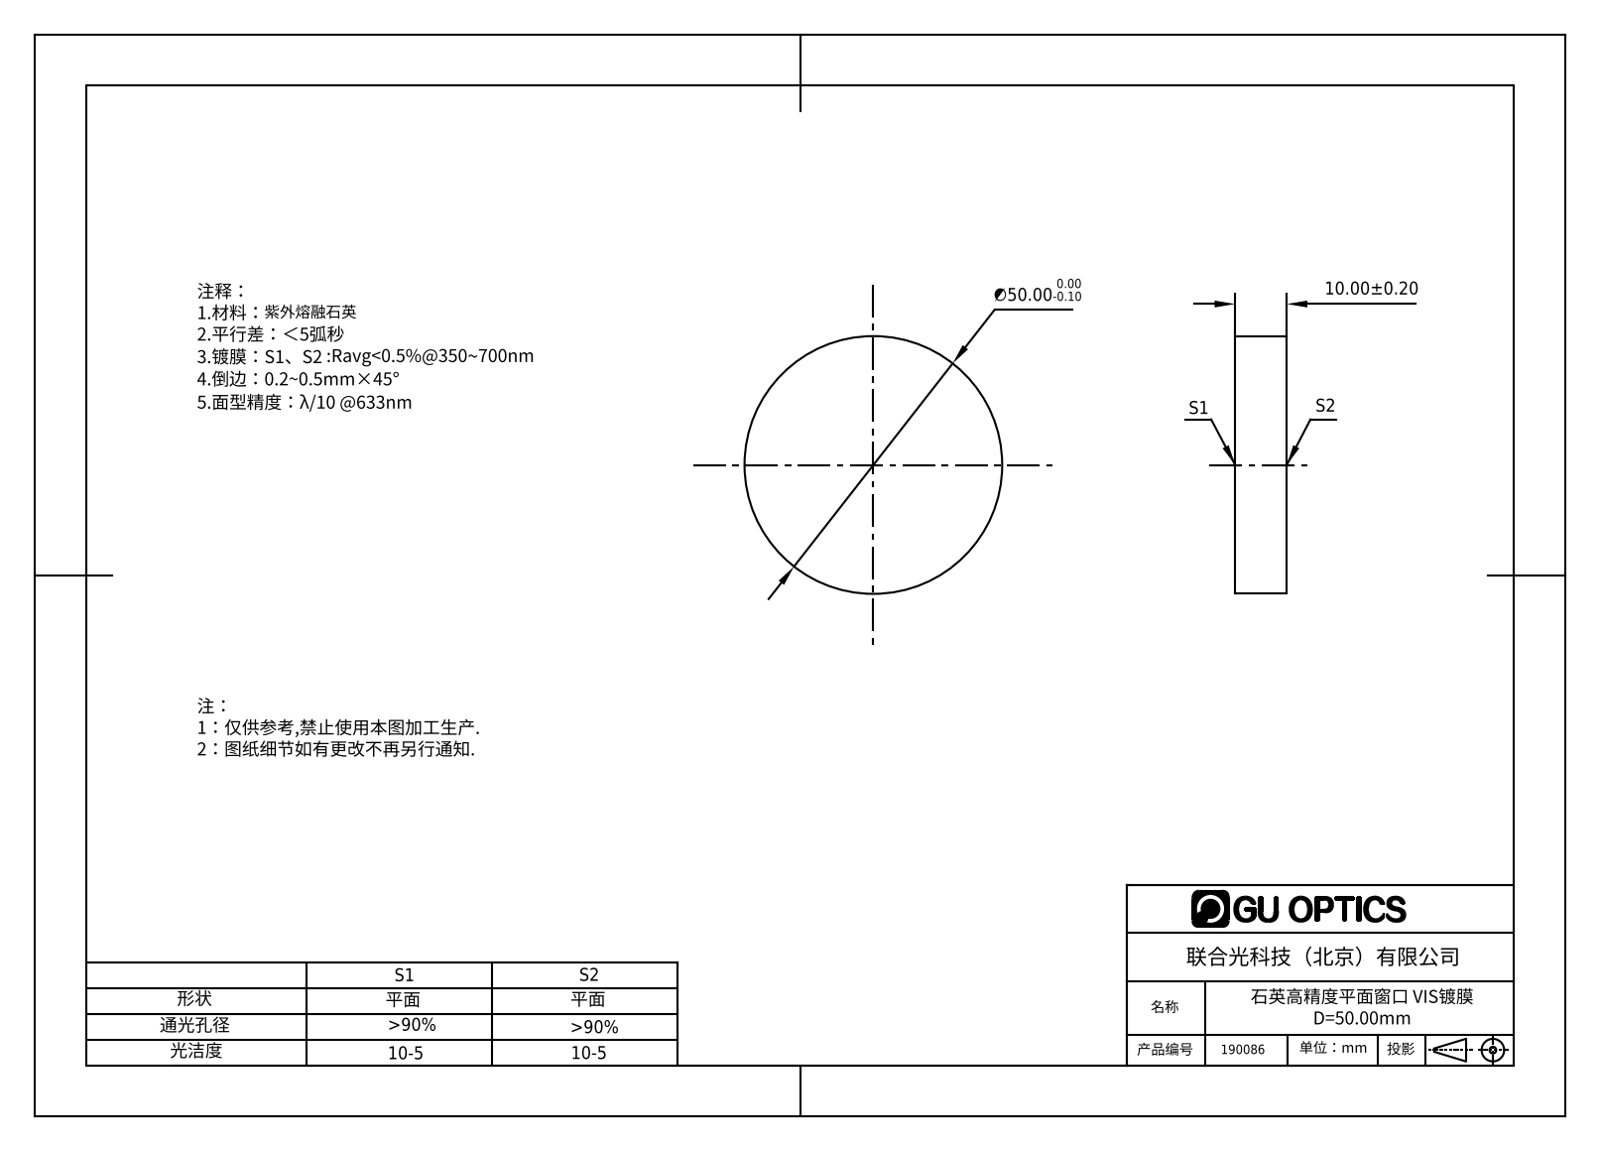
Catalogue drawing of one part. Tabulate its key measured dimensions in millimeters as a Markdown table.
| quantity | value |
| --- | --- |
| part name | 190064 |
| STEP written by | SolidWorks 2016 (AUTOMOTIVE_DESIGN) |
| units | millimeters |
| bodies | 1 solid, 4 faces (2 planar, 2 cylindrical, 0 other) |
| overall size | 50 × 50 × 10 |
| volume | 19 635 mm³ |
| surface area | 5 498 mm² |
| round bosses / shafts (diameter × count) | 50 × 1 |
| main face-to-face distances | 10 |
